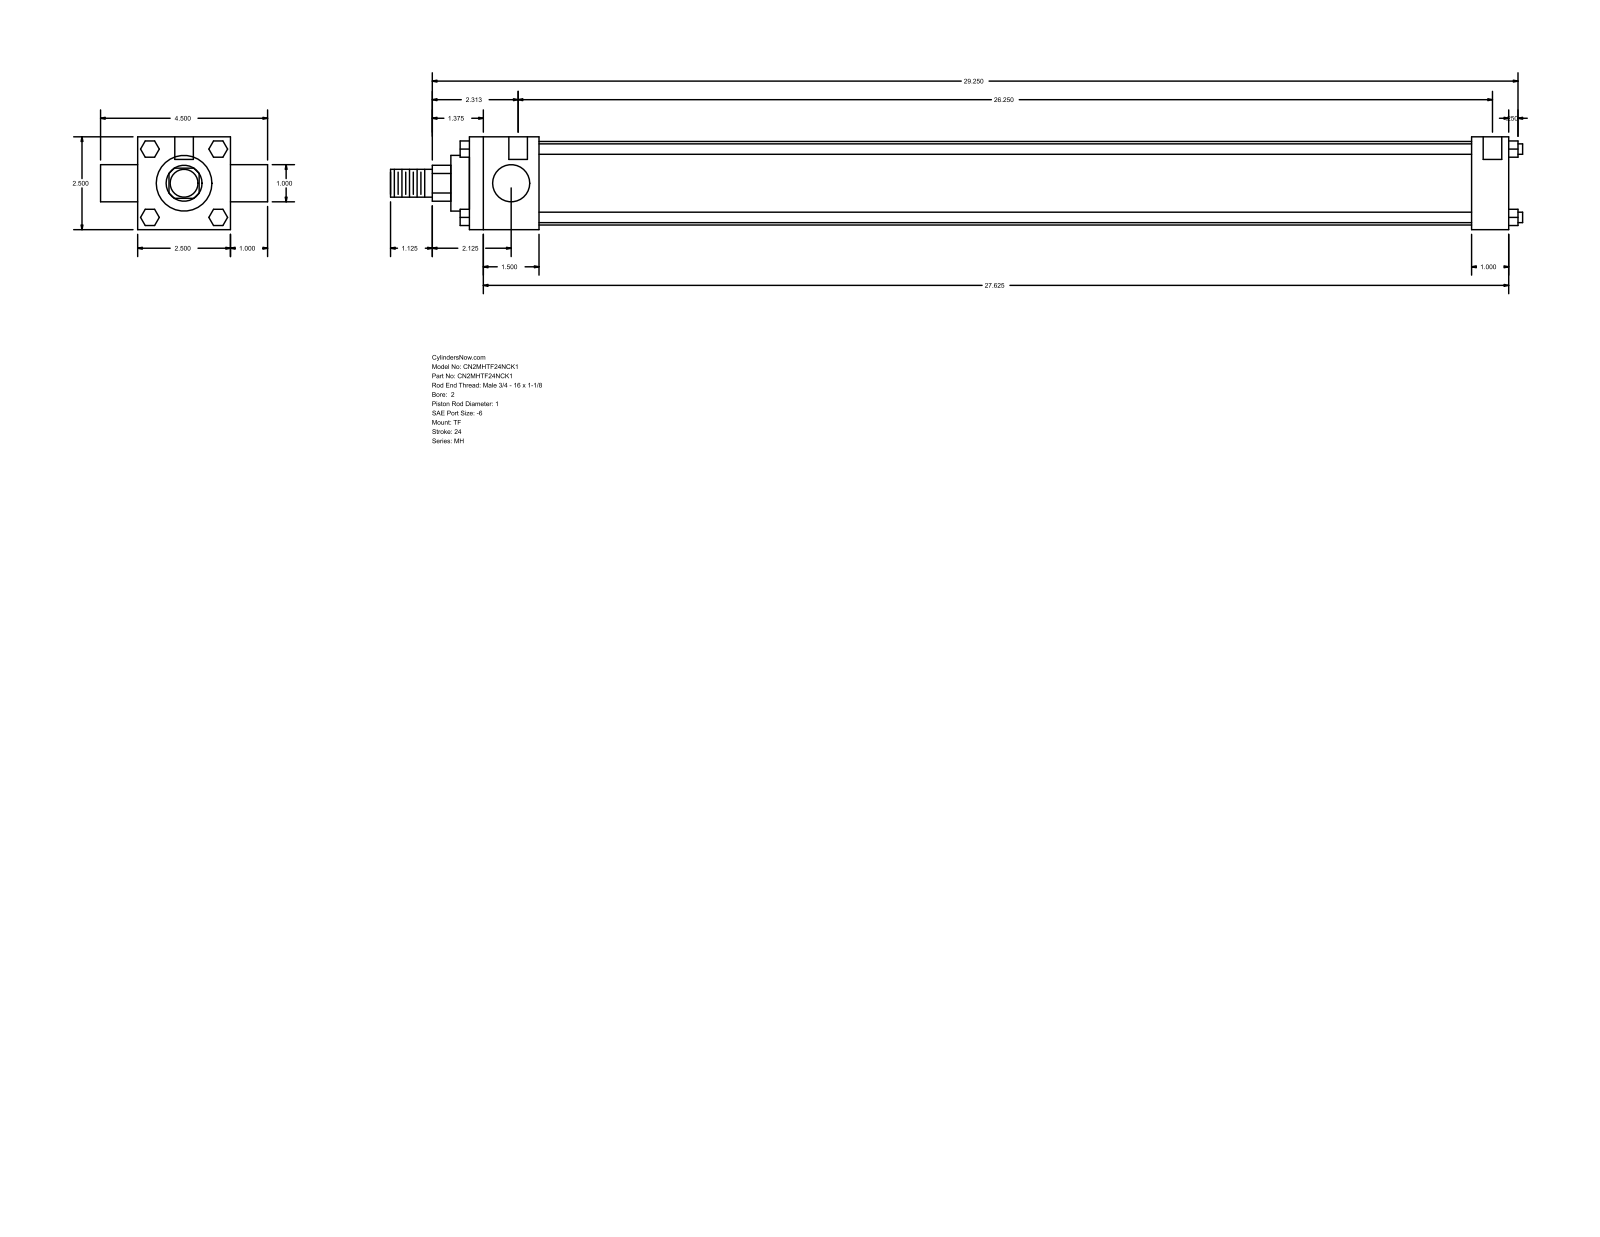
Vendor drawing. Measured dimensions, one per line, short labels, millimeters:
name: MH_TF__0200_1
written by: GSSL Pune (CONFIG_CONTROL_DESIGN)
unit: mm
bodies: 0 solids, 120 faces (92 planar, 28 cylindrical, 0 other)
size: 774.7 × 114.3 × 63.5
holes: 3× ⌀5.56, 2× ⌀12.7
bosses: 4× ⌀7.14, 2× ⌀25.4, 1× ⌀57.15, 1× ⌀38.1, 1× ⌀19.05
rounds: 1× R12.29
face distances: 63.5, 711.2, 25.4, 47.63, 685.8, 638.17, 663.57, 88.9, 723.9, 6.35
hole spacings: 3.17, 4.76, 666.75, 669.92, 671.51, 674.68
